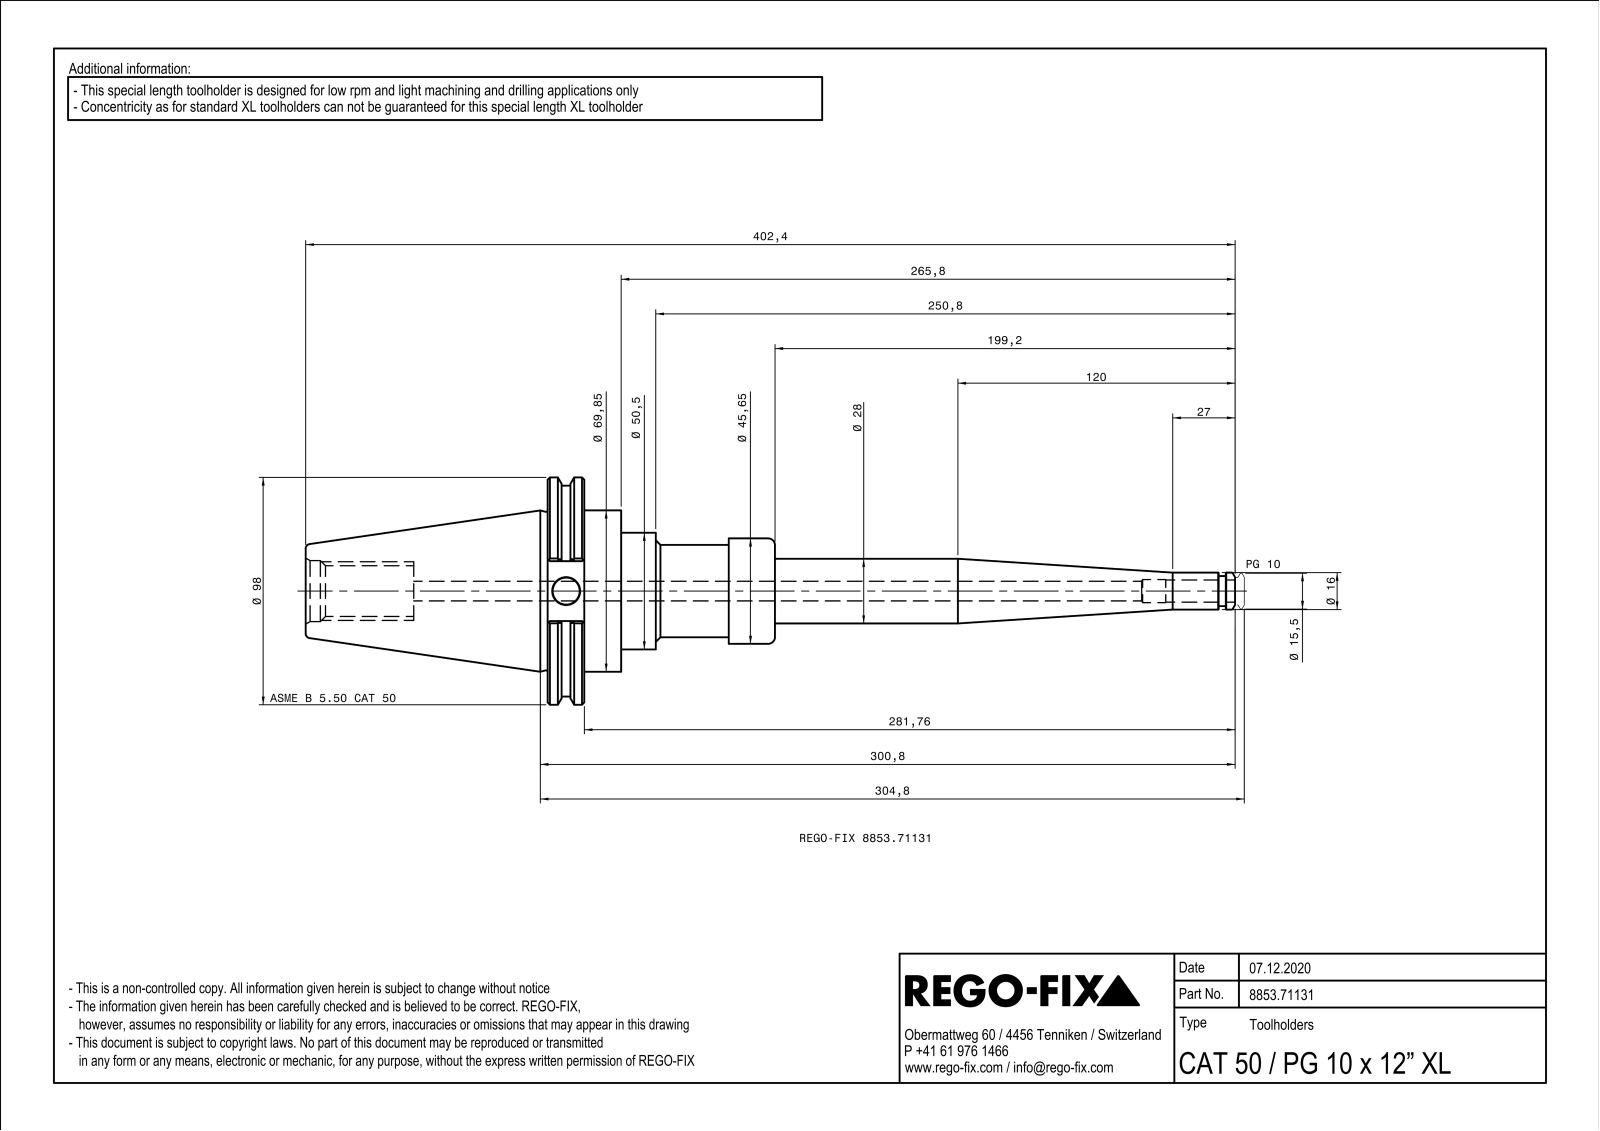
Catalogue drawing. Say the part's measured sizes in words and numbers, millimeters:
The part is named "NOCUT". Its 3-D file was written by "SIEMENS PLM Software Solid Edge ST10 (AUTOMOTIVE_DESIGN)". It is 1 solid with 166 faces: 48 planar, 44 cylindrical and 74 other. Overall it measures 402.4 by 98.42 by 94.39 millimeters. Its volume is 537 558 cubic millimeters and its surface area 87 738 square millimeters. Round holes: 1 of diameter 9, 1 of diameter 10, 1 of diameter 11.7, 1 of diameter 21.96, 1 of diameter 25, 1 of diameter 26.4, 1 of diameter 29, 1 of diameter 38.38, 1 of diameter 40.05, 1 of diameter 43.3. Round bosses or shafts: 1 of diameter 98.42, 1 of diameter 91.3, 1 of diameter 69.85, 1 of diameter 50.5, 1 of diameter 45.65, 1 of diameter 40, 1 of diameter 34, 1 of diameter 33. Partial cylindrical surfaces (rounded edges, fillets, slot ends): 12 of radius 0.5, 1 of radius 22.77. The main face-to-face distances are 15.87, 15.96, 31.83, 66.6, 82.56, 98.43, 6, 14, 203.2, 136.6.
